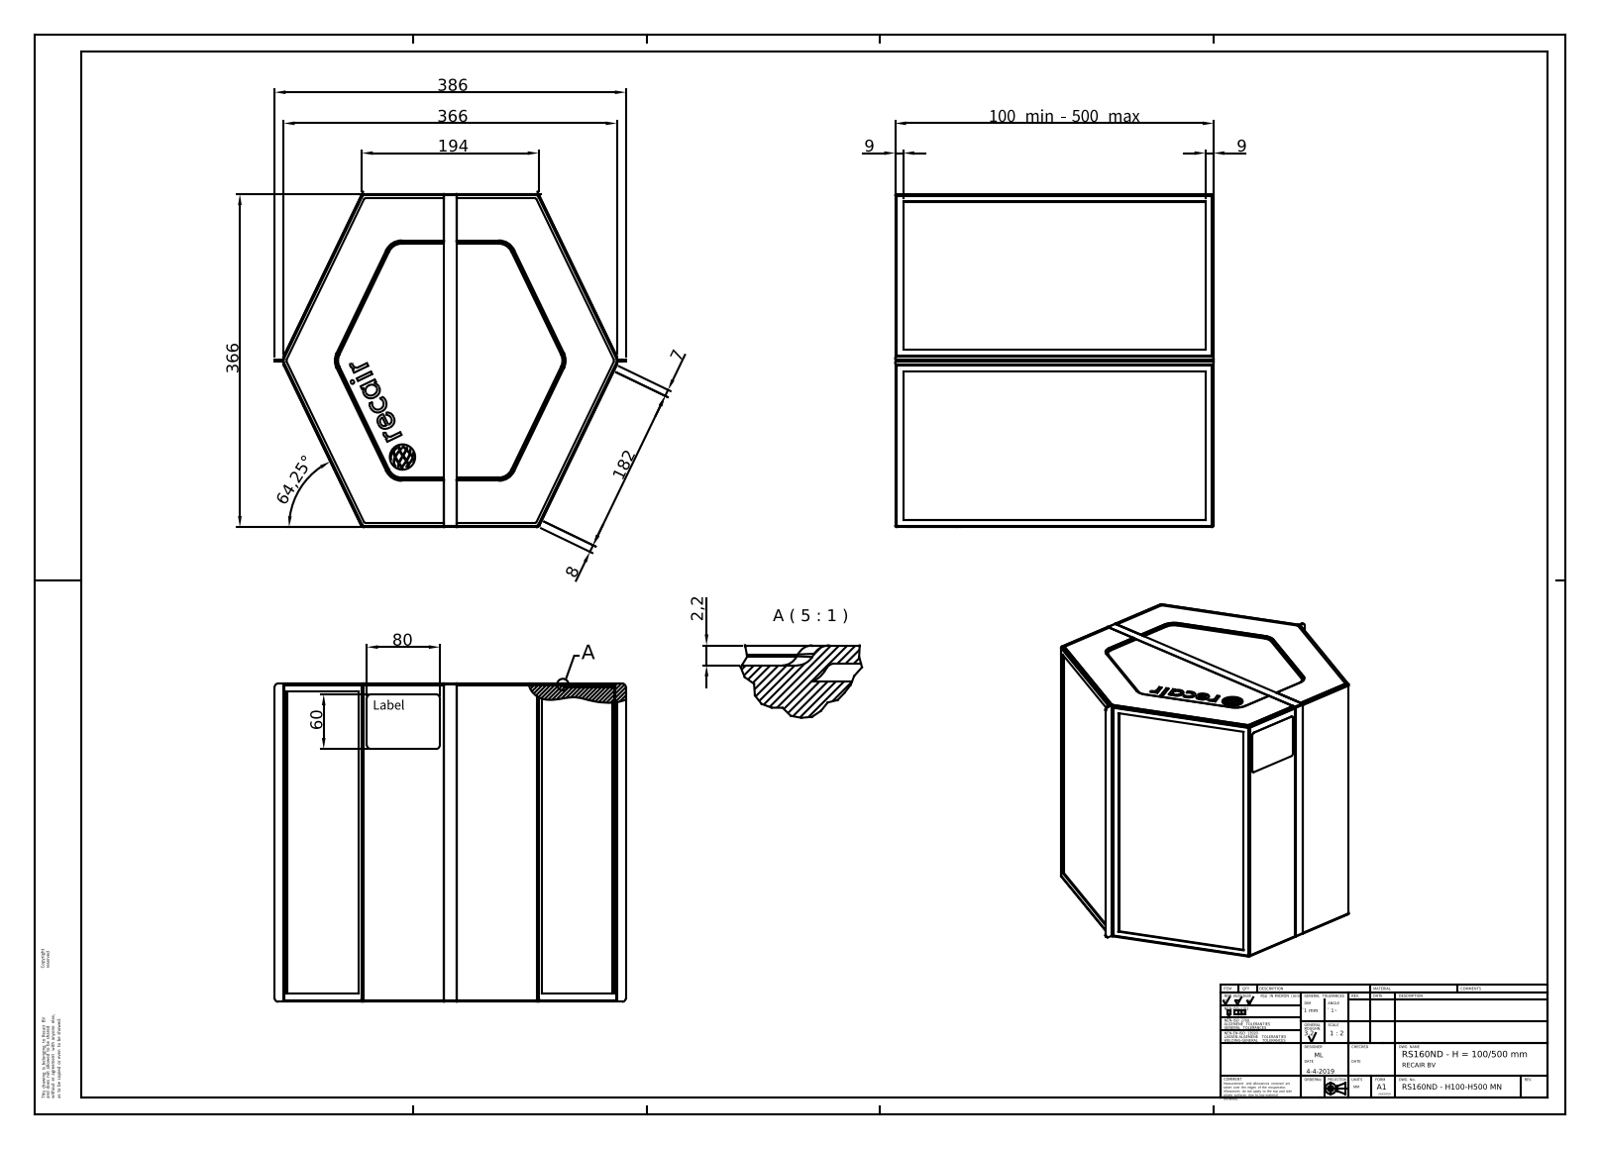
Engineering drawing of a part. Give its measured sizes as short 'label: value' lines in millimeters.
name: RS160ND - H100-H500 MN
written by: Autodesk Inventor 2019 (AUTOMOTIVE_DESIGN)
unit: mm
bodies: 1 solid, 2271 faces (1321 planar, 274 cylindrical, 676 other)
size: 386 × 366.05 × 350
volume: 34 840 000 mm³; area: 1 209 000 mm²
bosses: 2× ⌀27.86
rounds: 54× R0.47, 28× R2, 28× R3, 20× R0.2, 16× R1, 16× R1.5, 14× R0.48, 12× R20
face distances: 1.8, 2, 346, 1, 2.8, 363.2, 361.4, 364.2, 2.2, 4
